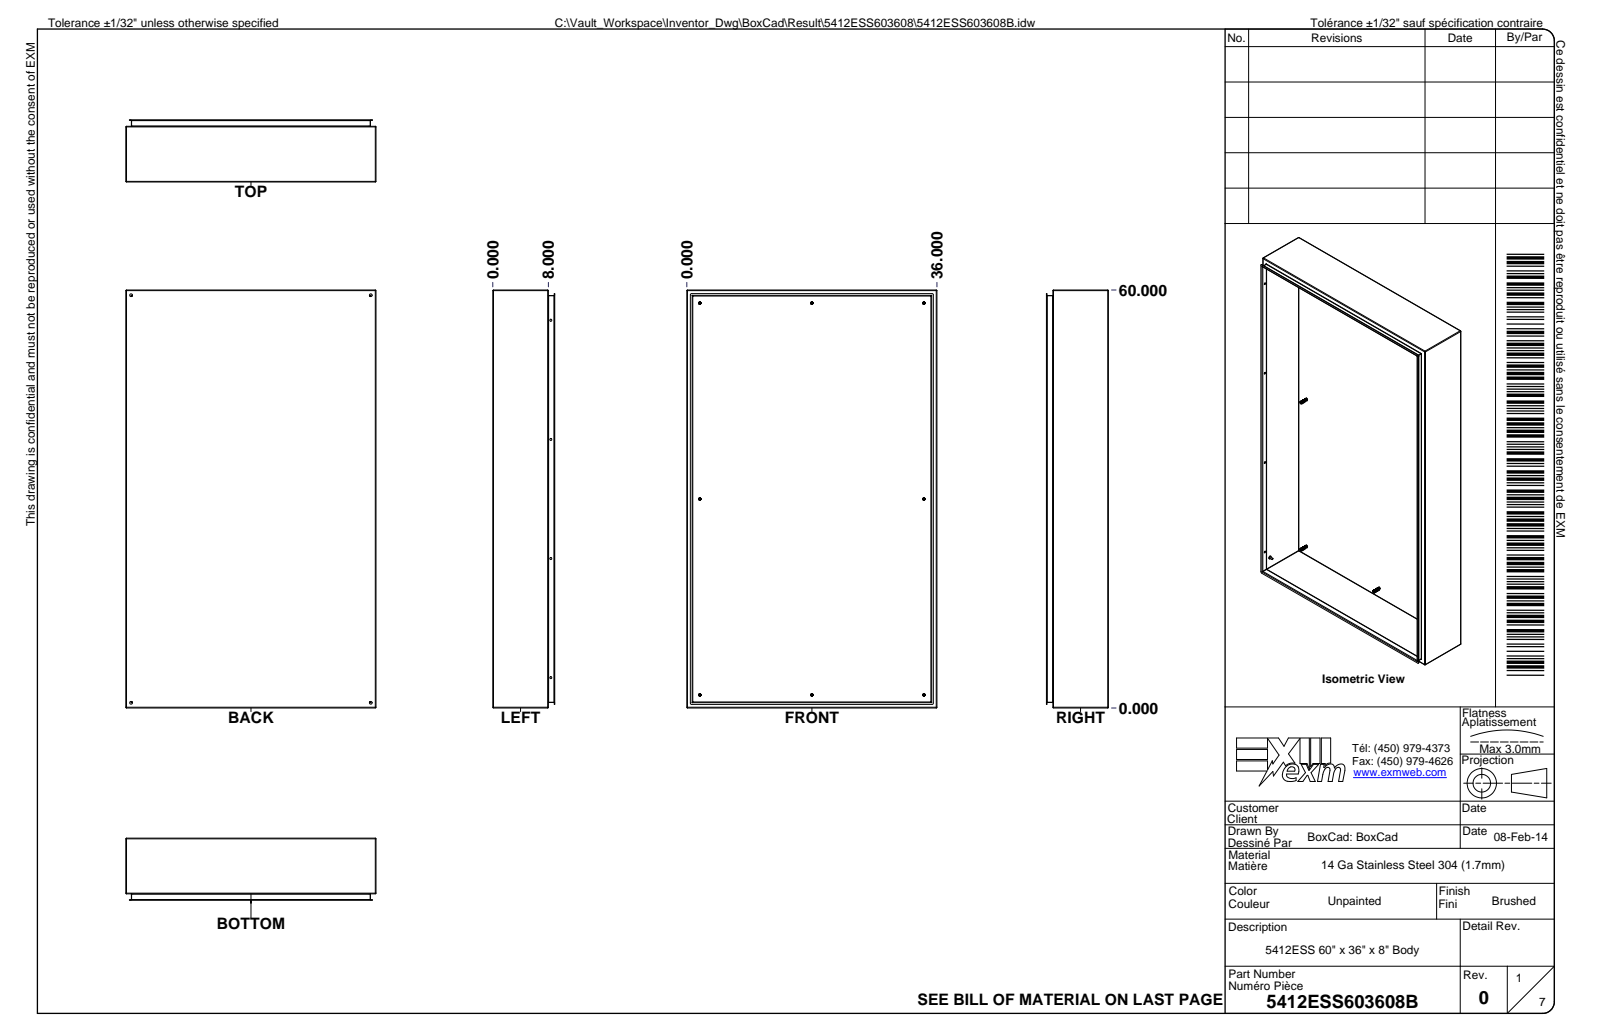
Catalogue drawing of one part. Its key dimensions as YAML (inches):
part_name: "5412ESS603608; 5412ESS603608B; 5412ESS603608B-P; STK-Q-16020 (+8 more)"
step_written_by: "Autodesk Inventor 2024 (AUTOMOTIVE_DESIGN)"
units: inches
bodies: {solids: 123, faces: 20687, planar: 6380, cylindrical: 4307, other: 10000}
overall_size: [60, 36.007, 10.985]
volume: 682.5
surface_area: 17781
round_holes:
  - {diameter: 0.165, count: 112}
  - {diameter: 0.03, count: 18}
  - {diameter: 0.315, count: 14}
  - {diameter: 0.201, count: 13}
  - {diameter: 0.311, count: 11}
  - {diameter: 0.044, count: 8}
  - {diameter: 0.27, count: 8}
  - {diameter: 0.29, count: 8}
  - {diameter: 0.197, count: 6}
  - {diameter: 0.268, count: 6}
  - {diameter: 0.5, count: 5}
  - {diameter: 0.236, count: 4}
round_bosses_or_shafts:
  - {diameter: 0.237, count: 112}
  - {diameter: 0.03, count: 18}
  - {diameter: 0.232, count: 17}
  - {diameter: 0.039, count: 16}
  - {diameter: 0.717, count: 8}
  - {diameter: 0.311, count: 8}
  - {diameter: 0.262, count: 8}
  - {diameter: 0.177, count: 7}
partial_cylinders:
  - {radius: 0.02, count: 247}
  - {radius: 0.039, count: 241}
  - {radius: 0.01, count: 170}
  - {radius: 0.008, count: 122}
  - {radius: 0.079, count: 55}
  - {radius: 0.059, count: 42}
  - {radius: 0.016, count: 37}
  - {radius: 0.012, count: 36}
face_to_face_distances: [0.068, 9.052, 8.984, 9.12, 8.178, 0.942, 0.874, 8.11, 0.105, 1.047]
hole_center_spacings: [1.969, 0.984, 2.953, 3.937, 17.101, 34.202, 4.921, 1.591]
